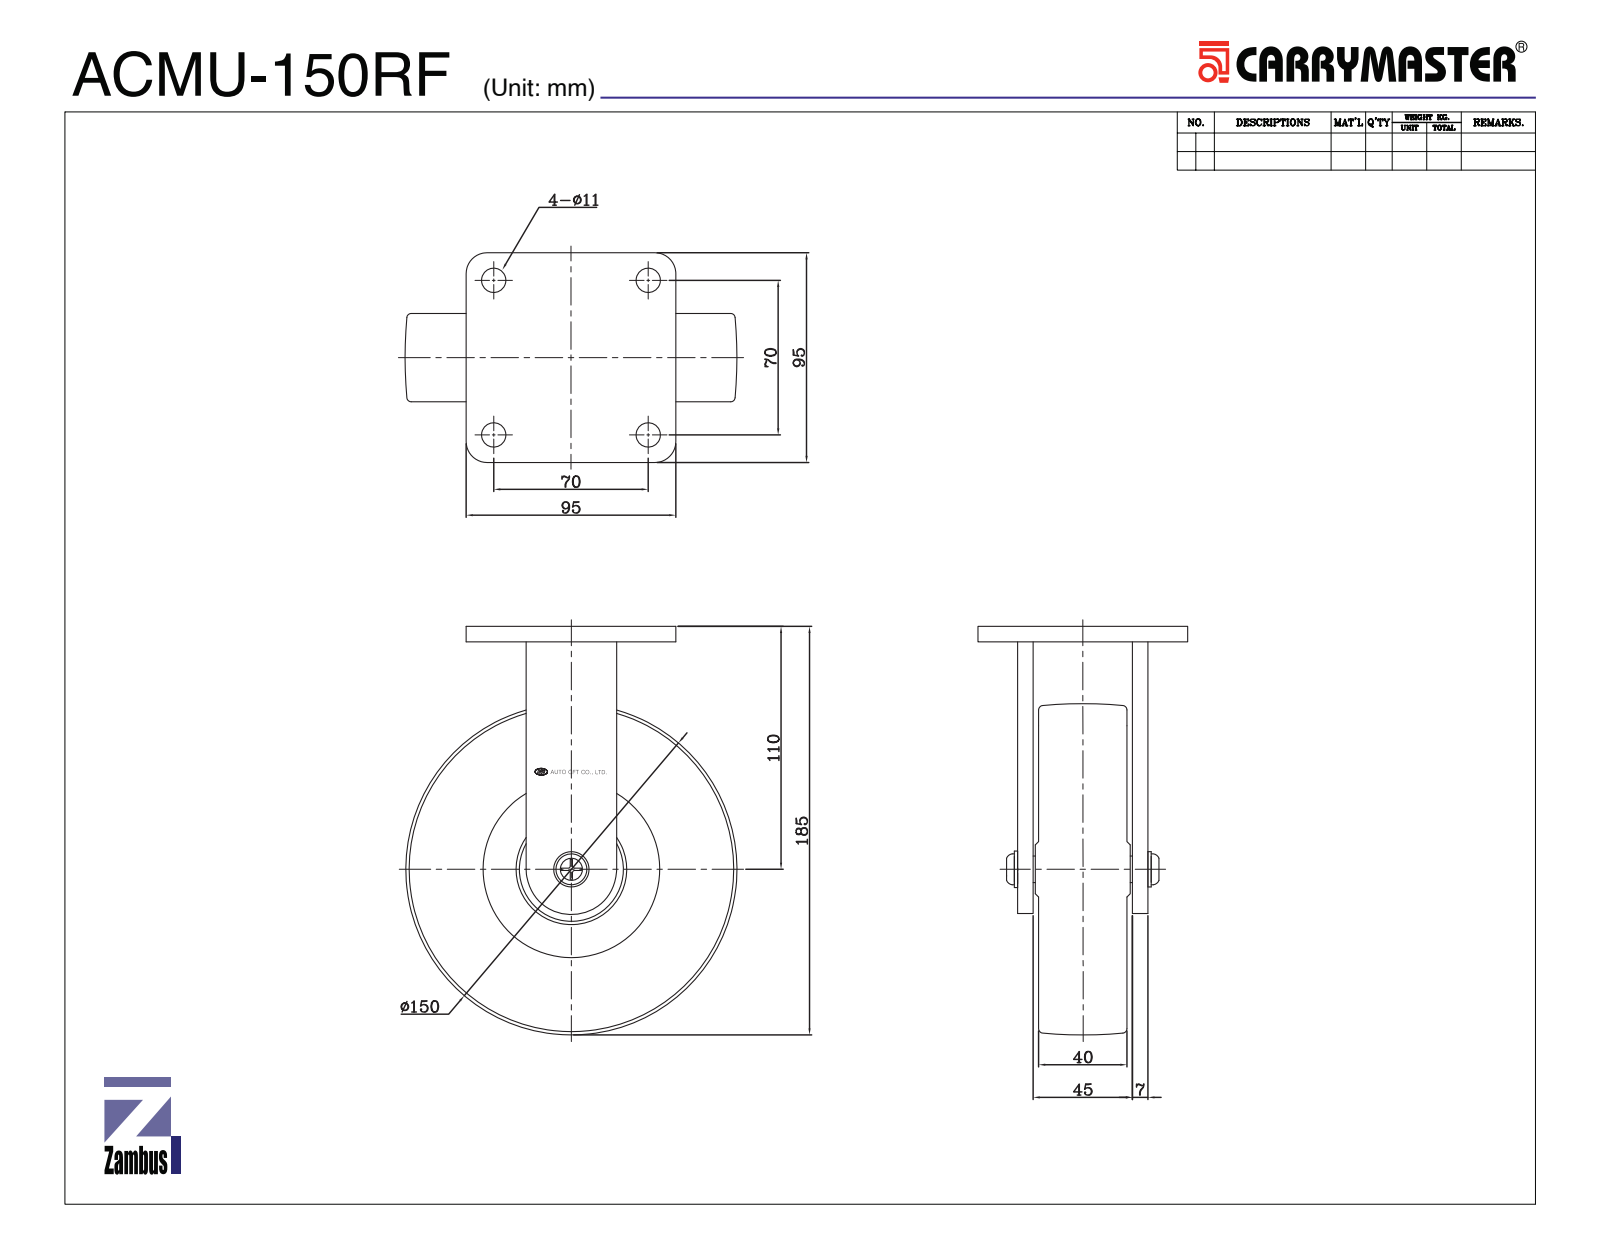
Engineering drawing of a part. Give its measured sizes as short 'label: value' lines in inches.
name: ACMU-150RF
written by: SolidWorks 2015 (CONFIG_CONTROL_DESIGN)
unit: in
bodies: 10 solids, 1348 faces (529 planar, 133 cylindrical, 686 other)
size: 7.283 × 5.906 × 3.74
volume: 35.81 in³; area: 259.6 in²
holes: 4× ⌀0.433, 1× ⌀0.268, 1× ⌀0.472, 1× ⌀0.484, 1× ⌀0.773, 1× ⌀0.887, 1× ⌀1.179
bosses: 1× ⌀5.906, 1× ⌀1.457, 1× ⌀1.042, 1× ⌀0.75, 1× ⌀0.63, 1× ⌀0.551, 1× ⌀0.315
rounds: 16× R0.157, 10× R0.039, 4× R0.374, 2× R0.02, 1× R0.72, 1× R0.807
face distances: 0.276, 0.394, 1.575, 2.047, 1.969, 0.295, 1.693, 0.492, 1.772, 1.181
hole spacings: 2.756, 3.897
